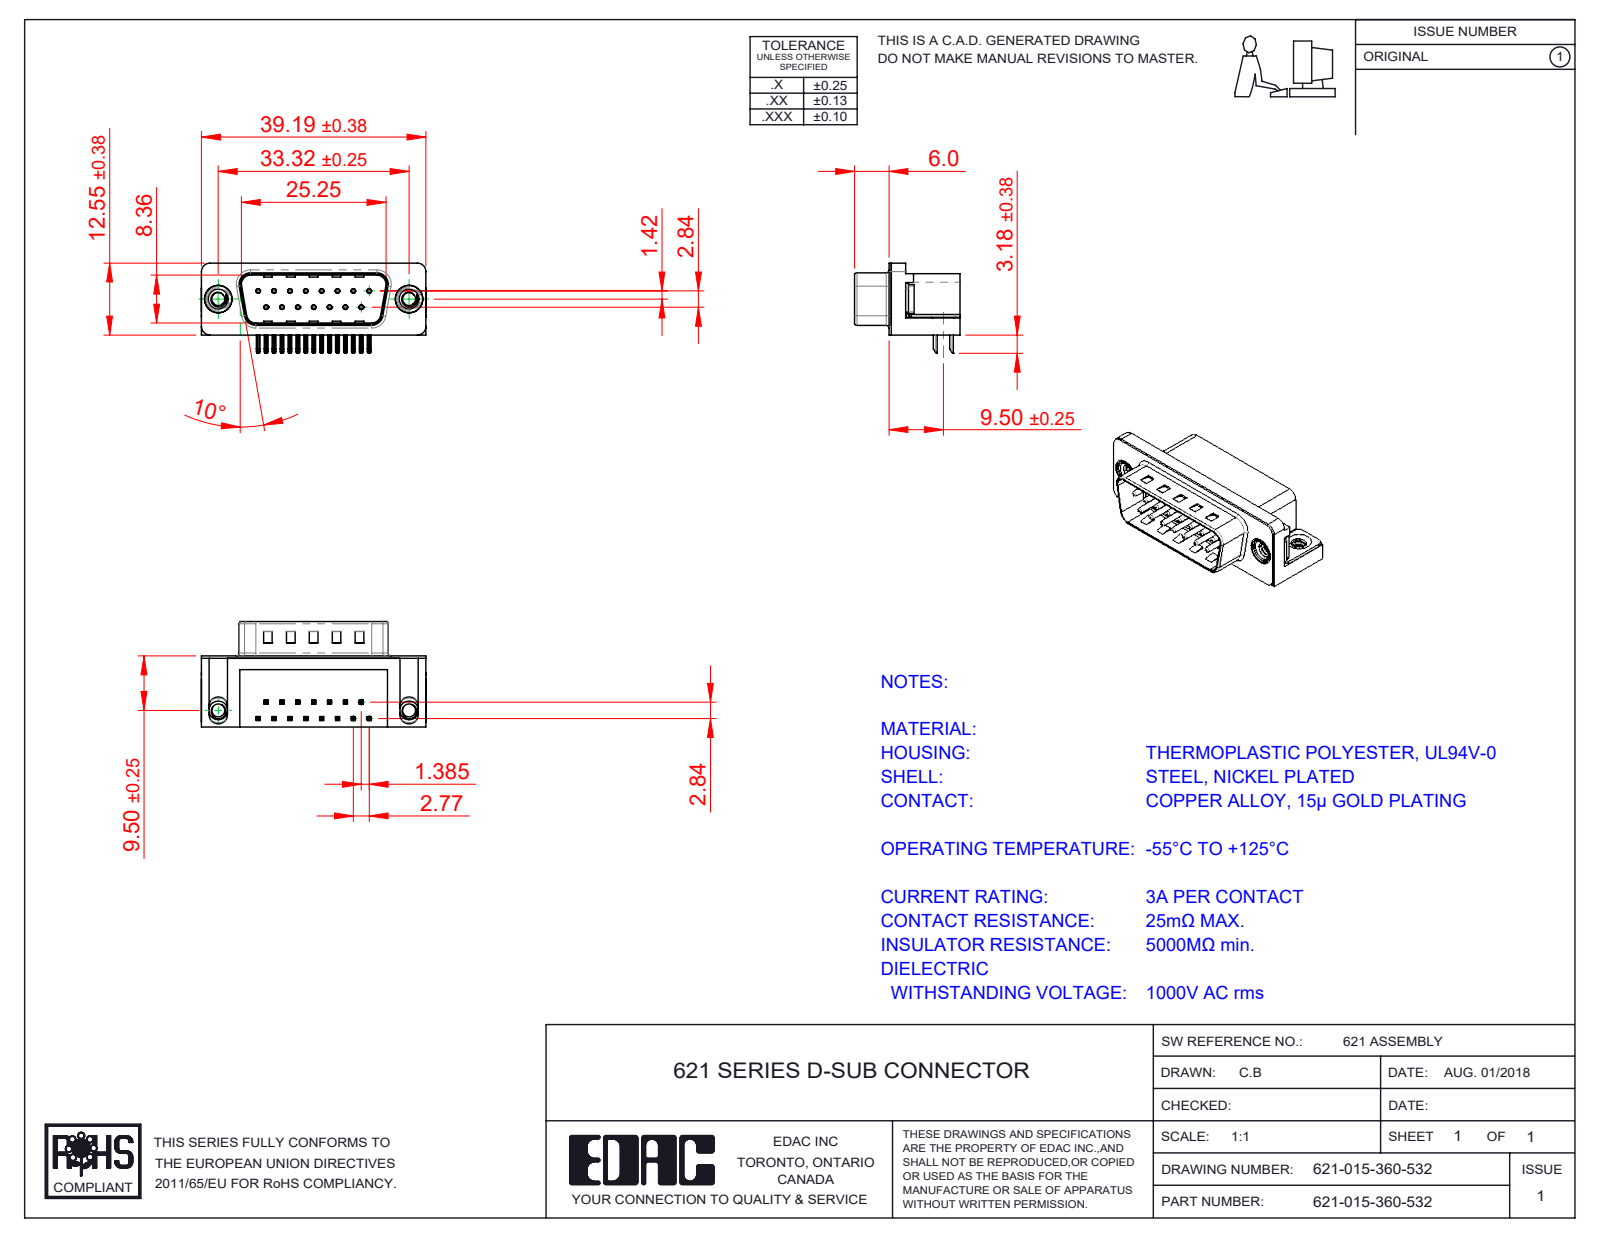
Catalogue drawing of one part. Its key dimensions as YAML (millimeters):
part_name: "621 2 Prong Board Lock; 621 Contact Bottom; 621 4-40 Threaded Rivet; 621 Contact Top (+3 more)"
step_written_by: "SolidWorks 2016 (CONFIG_CONTROL_DESIGN)"
units: millimeters
bodies: {solids: 21, faces: 1517, planar: 925, cylindrical: 453, other: 139}
overall_size: [39.22, 18.4, 16.25]
volume: 4415
surface_area: 5656
round_holes:
  - {diameter: 0.35, count: 15}
  - {diameter: 0.8, count: 15}
  - {diameter: 2.26, count: 2}
  - {diameter: 4, count: 2}
  - {diameter: 4.8, count: 2}
  - {diameter: 5, count: 2}
round_bosses_or_shafts:
  - {diameter: 0.75, count: 15}
  - {diameter: 4.9, count: 2}
  - {diameter: 4.75, count: 2}
  - {diameter: 3.9, count: 2}
partial_cylinders:
  - {radius: 0.25, count: 68}
  - {radius: 0.12, count: 30}
  - {radius: 1, count: 16}
  - {radius: 0.5, count: 14}
  - {radius: 1.6, count: 8}
  - {radius: 1.5, count: 6}
  - {radius: 0.32, count: 4}
  - {radius: 0.9, count: 4}
face_to_face_distances: [0.4, 12, 10.35, 2.1, 10.46, 12.4, 1.7, 10.86, 8.76, 9.5]
hole_center_spacings: [3.16, 2.77, 5.54, 8.31, 11.08, 5.03, 5.04, 7.48]
